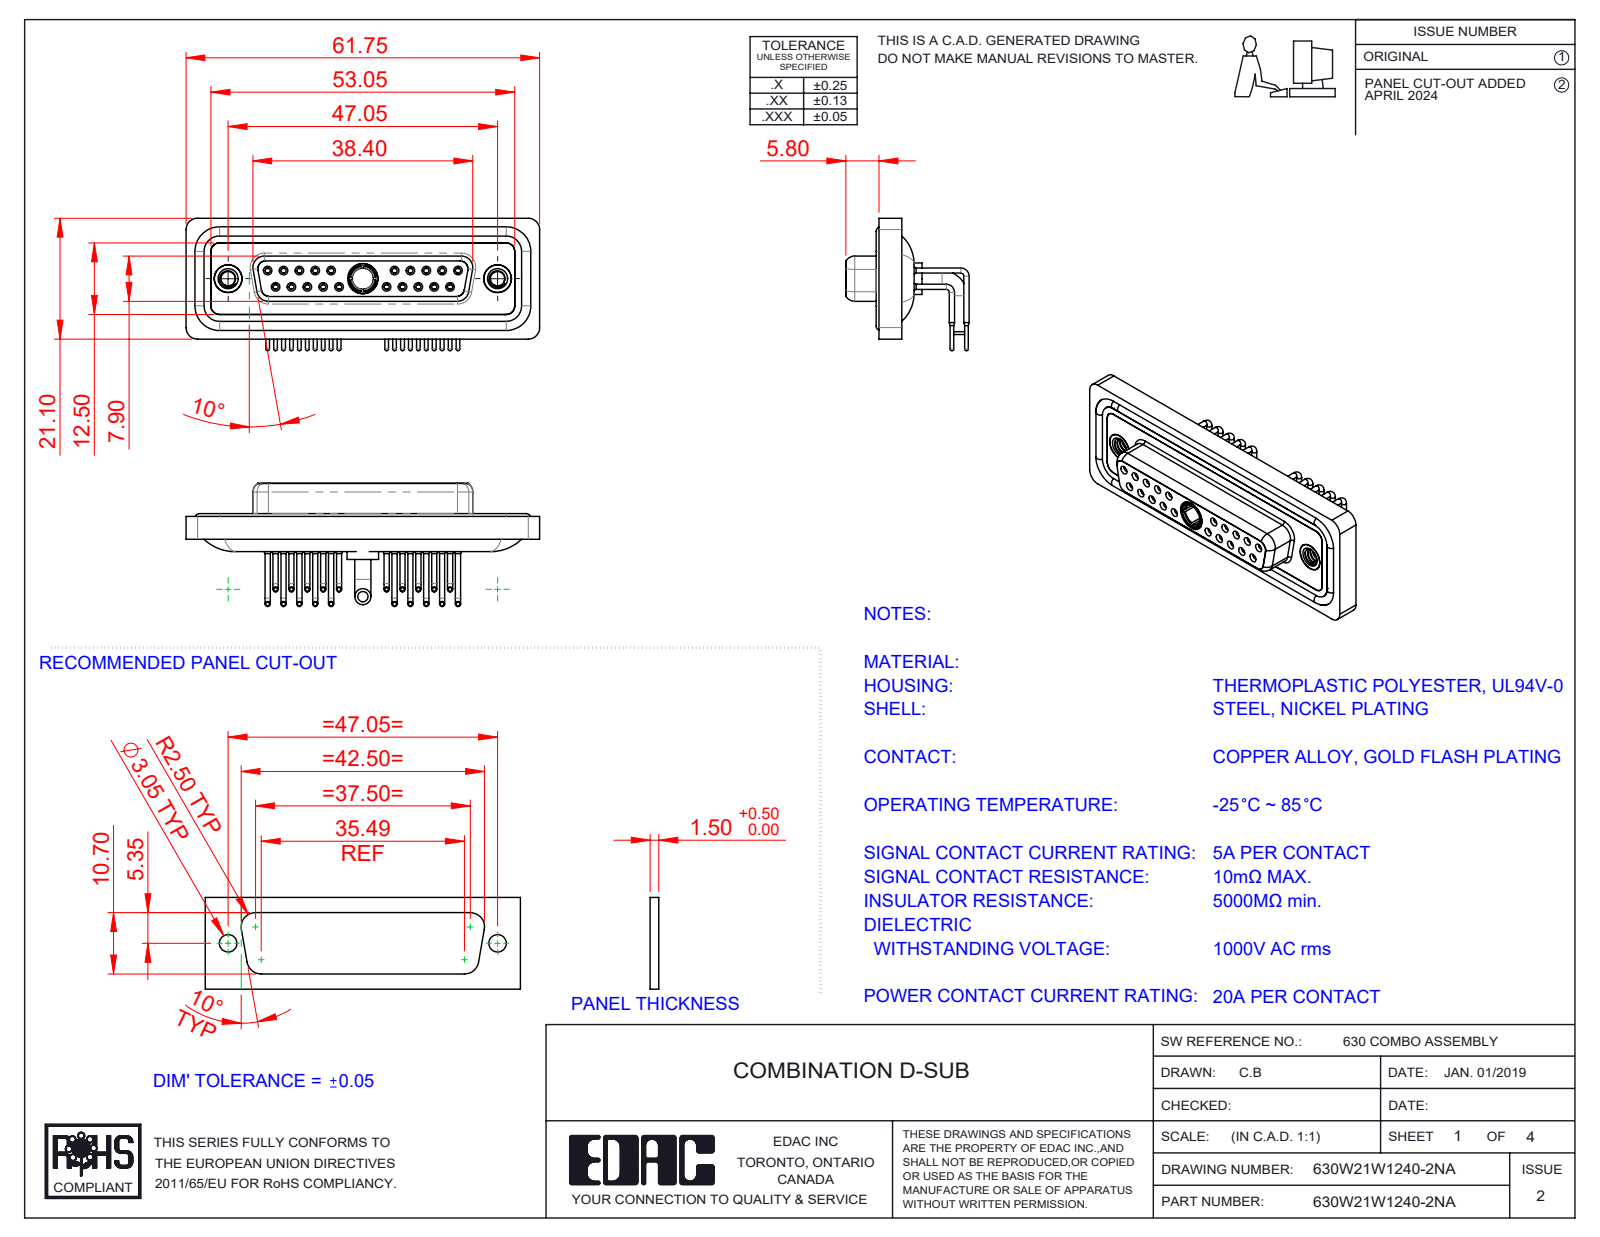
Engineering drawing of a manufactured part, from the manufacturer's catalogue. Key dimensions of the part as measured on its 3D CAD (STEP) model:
Part name (STEP PRODUCT): 630Combo Shell Front_25 Contacts; 630Combo Housing_21W1; 630Combo Threaded Rivet_A; Power Socket_20A RA (+5 more)
STEP written by: SolidWorks 2023 (CONFIG_CONTROL_DESIGN)
Units: millimetres
Bodies: 29 solids, 1518 faces (434 planar, 671 cylindrical, 413 other)
Overall size (bounding box): 61.75 × 23.12 × 21.53
Volume: 8 498 mm³ · Surface area: 14 783 mm²
Round holes (diameter × count): ⌀0.9 ×20, ⌀1.1 ×20, ⌀1.5 ×20, ⌀2 ×20, ⌀1.6 ×10, ⌀1.7 ×10, ⌀4.85 ×3, ⌀2.5 ×2, ⌀4 ×2, ⌀4.05 ×2, ⌀5 ×2, ⌀3.7 ×1
Round bosses / shafts (diameter × count): ⌀0.9 ×20, ⌀0.65 ×20, ⌀1.6 ×14, ⌀4.95 ×2, ⌀4.8 ×2, ⌀2.8 ×2, ⌀5.5 ×1, ⌀5.2 ×1
Partial cylindrical surfaces — rounded edges, fillets, slot ends (radius × count): R1.5 ×18, R2 ×18, R1.35 ×8, R1.6 ×8, R0.25 ×4, R0.5 ×4, R0.6 ×4, R0.65 ×4
Main face-to-face distances: 0.4, 1.8, 4.1, 1.6, 1.1, 2.5, 3.1, 1.5, 9.8, 0.45
Hole centre spacings: 3.16, 2.77, 5.54, 8.31, 5.04, 19.39, 20.97, 22.16
